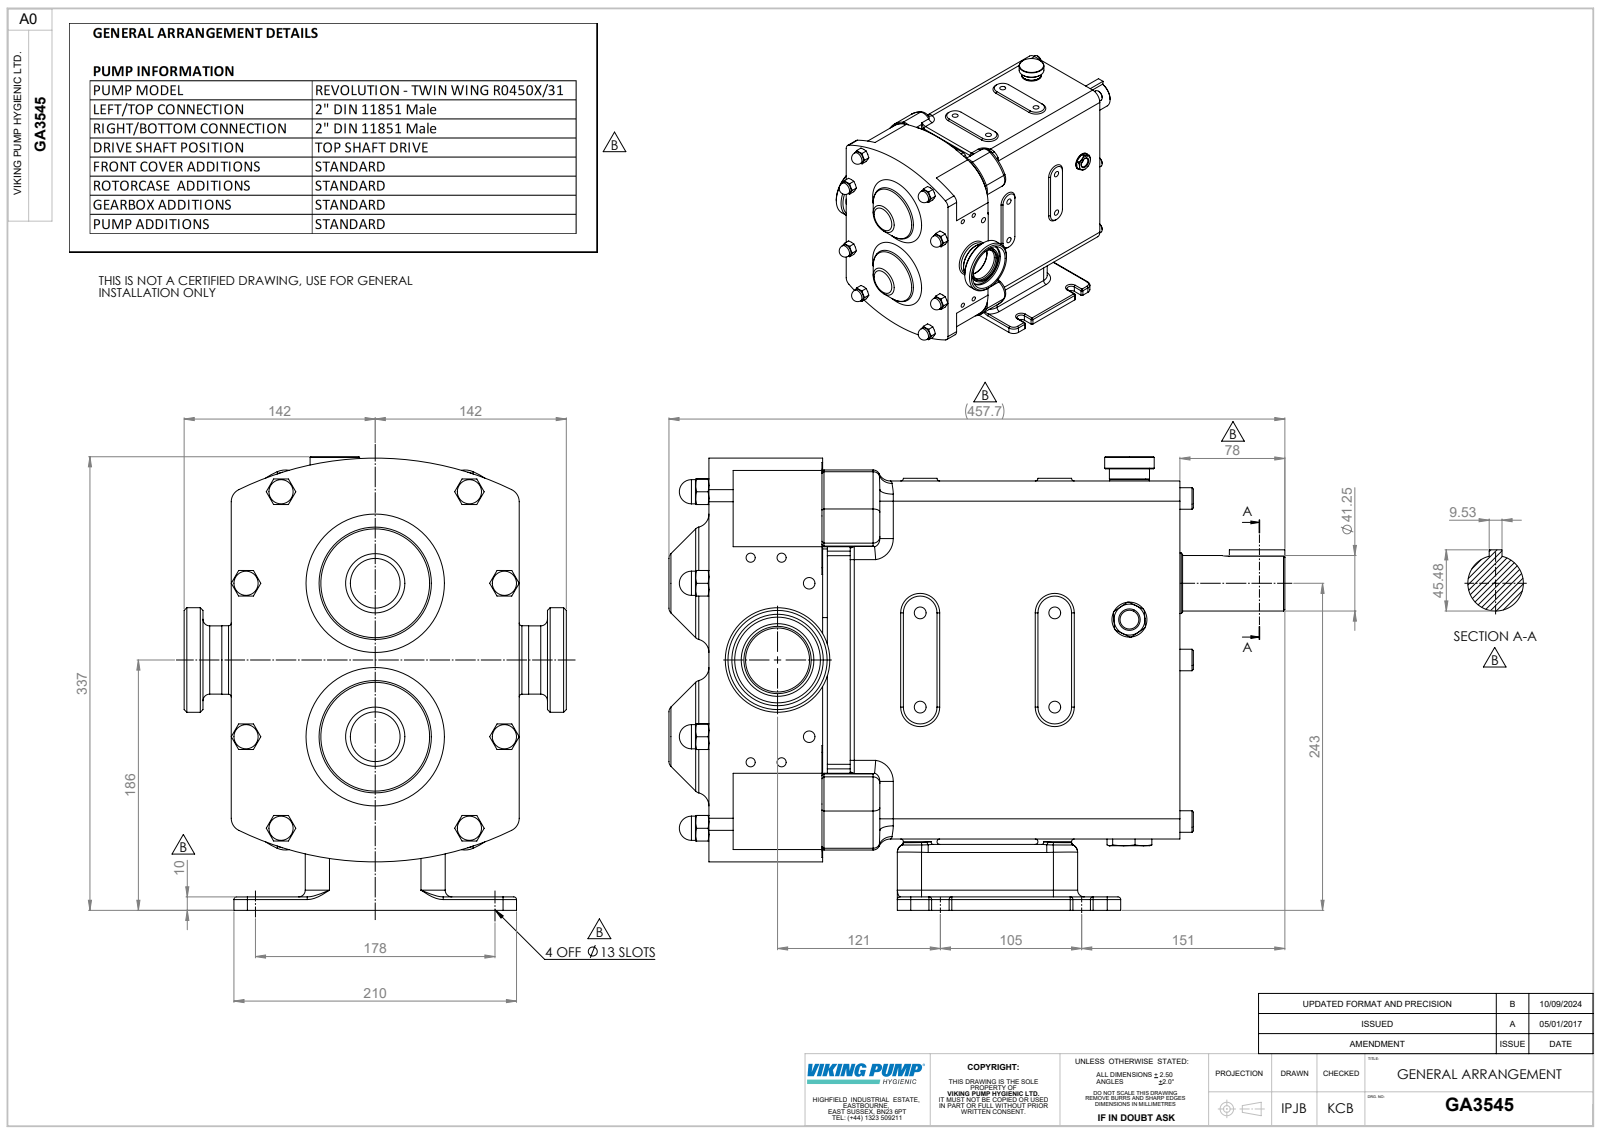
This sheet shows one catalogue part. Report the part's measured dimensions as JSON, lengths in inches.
{"part_name": "Copy of R0450 CPP H TSD^GA3545; GA3545; Copy of Z94-5031-33 - 2 INCH DIN11851^GA3545", "step_written_by": "SolidWorks 2023 (AUTOMOTIVE_DESIGN)", "units": "inches", "bodies": {"solids": 3, "faces": 950, "planar": 295, "cylindrical": 290, "other": 365}, "overall_size": [18.02, 13.268, 11.181], "volume_in3": 1010, "surface_area_in2": 1071, "round_holes": [[0.346, 8], [0.268, 4], [0.339, 2], [0.551, 1], [1.331, 1], [1.874, 1], [1.969, 1], [2.508, 1]], "round_bosses_or_shafts": [[0.709, 8], [0.63, 6], [3.059, 1], [2.126, 1], [2.008, 1], [2.004, 1], [1.996, 1], [1.772, 1]], "partial_cylinders_radius": [[0.079, 38], [0.394, 30], [0.197, 19], [0.232, 8], [0.591, 8], [0.709, 8], [0.118, 4], [0.236, 4]], "face_to_face_distances": [5.984, 3.327, 10.453, 13.78, 3.465, 0.138, 10.315, 10.472, 1.693, 7.205], "hole_center_spacings": [2.756, 3.937, 4.806, 0.906, 1.1, 1.869, 2.194, 2.427]}
